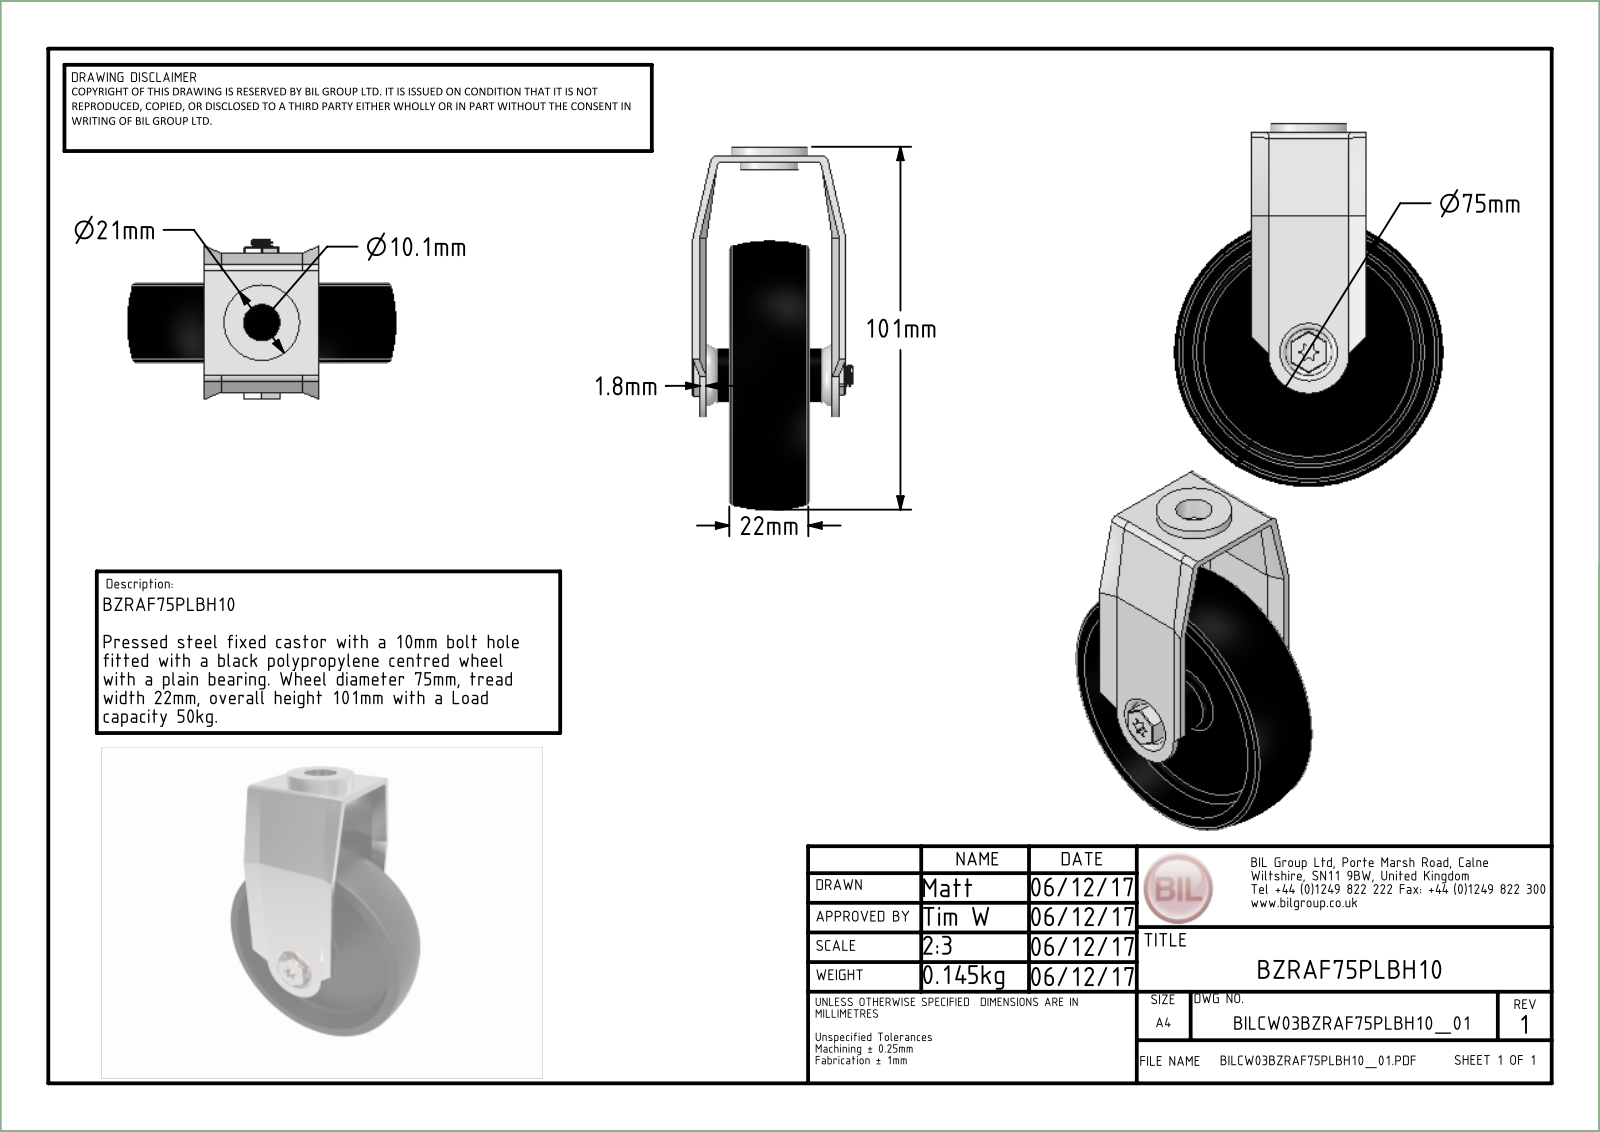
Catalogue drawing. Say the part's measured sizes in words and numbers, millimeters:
The part is named "BZRAF75PLBH10 v2; BZRAF75ASBH10 v1; ZINC PLATED PRESSED STEEL FORKS; BZA75WPL v1 (+7 more)". Its 3-D file was written by "Autodesk Translation Framework v13.20.0.188 (AP242_MANAGED_MODEL_BASED_3D_ENGINEERING_MIM_LF)". It is 5 solids with 273 faces: 74 planar, 97 cylindrical and 102 other. Overall it measures 101 by 75 by 44.75 millimeters. Its volume is 50 522 cubic millimeters and its surface area 34 035 square millimeters. Round holes: 1 of diameter 6, 1 of diameter 6.2, 1 of diameter 6.3, 1 of diameter 8.2, 1 of diameter 10.2, 1 of diameter 66. Round bosses or shafts: 1 of diameter 21, 1 of diameter 14, 1 of diameter 8, 1 of diameter 7.95, 1 of diameter 5.88, 1 of diameter 4.74. Partial cylindrical surfaces (rounded edges, fillets, slot ends): 26 of radius 1, 12 of radius 0.5, 8 of radius 1.5, 6 of radius 0.4, 4 of radius 0.99, 2 of radius 1.8, 1 of radius 2.12, 1 of radius 11.91. The main face-to-face distances are 1.8, 4, 35.8, 1, 7.3, 10, 14, 5.5, 15.5, 19.5.
